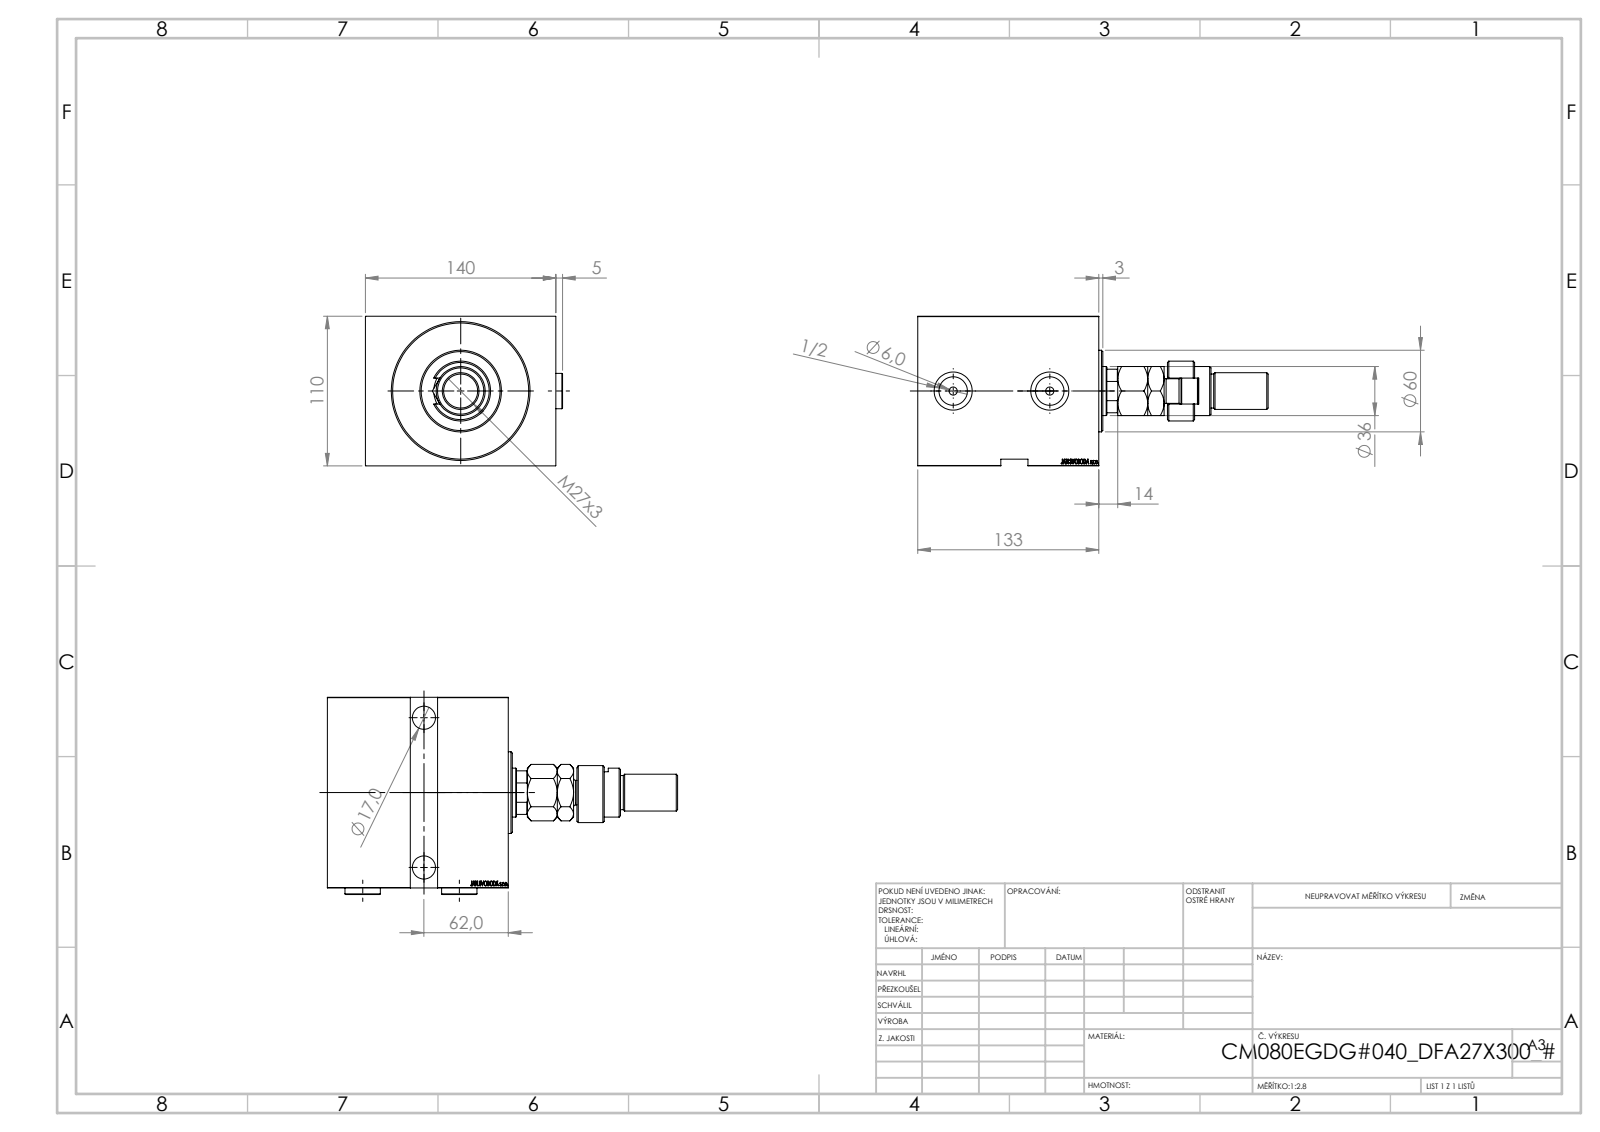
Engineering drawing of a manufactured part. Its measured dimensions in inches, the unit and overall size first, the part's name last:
Units: inches
Overall size (bounding box): 10.138 × 5.705 × 4.331
Round holes (diameter × count): ⌀0.236 ×2, ⌀0.669 ×2, ⌀0.825 ×2, ⌀0.984 ×2, ⌀1.102 ×2, ⌀1.004 ×1, ⌀1.555 ×1, ⌀3.15 ×1, ⌀3.937 ×1
Round bosses / shafts (diameter × count): ⌀1.024 ×2, ⌀3.228 ×1, ⌀2.362 ×1, ⌀1.732 ×1, ⌀1.417 ×1, ⌀1.102 ×1, ⌀1.063 ×1, ⌀0.984 ×1
Partial cylindrical surfaces — rounded edges, fillets, slot ends (radius × count): R0.374 ×1, R0.591 ×1, R0.689 ×1
Main face-to-face distances: 4.331, 5.512, 5.236, 0.827, 4.409, 0.197, 4.213, 5.039, 2.126, 3.11
Hole centre spacings: 2.795, 4.331
Volume: 116.6 in³ · Surface area: 345.2 in²
Bodies: 7 solids, 987 faces (472 planar, 73 cylindrical, 442 other)
Part name (STEP PRODUCT): V450CM_E_Body; V450CM_VC_B; V450CM_E_VCP; Zatka_OIL_PORT (+2 more)
STEP written by: SolidWorks 2019 (CONFIG_CONTROL_DESIGN)
